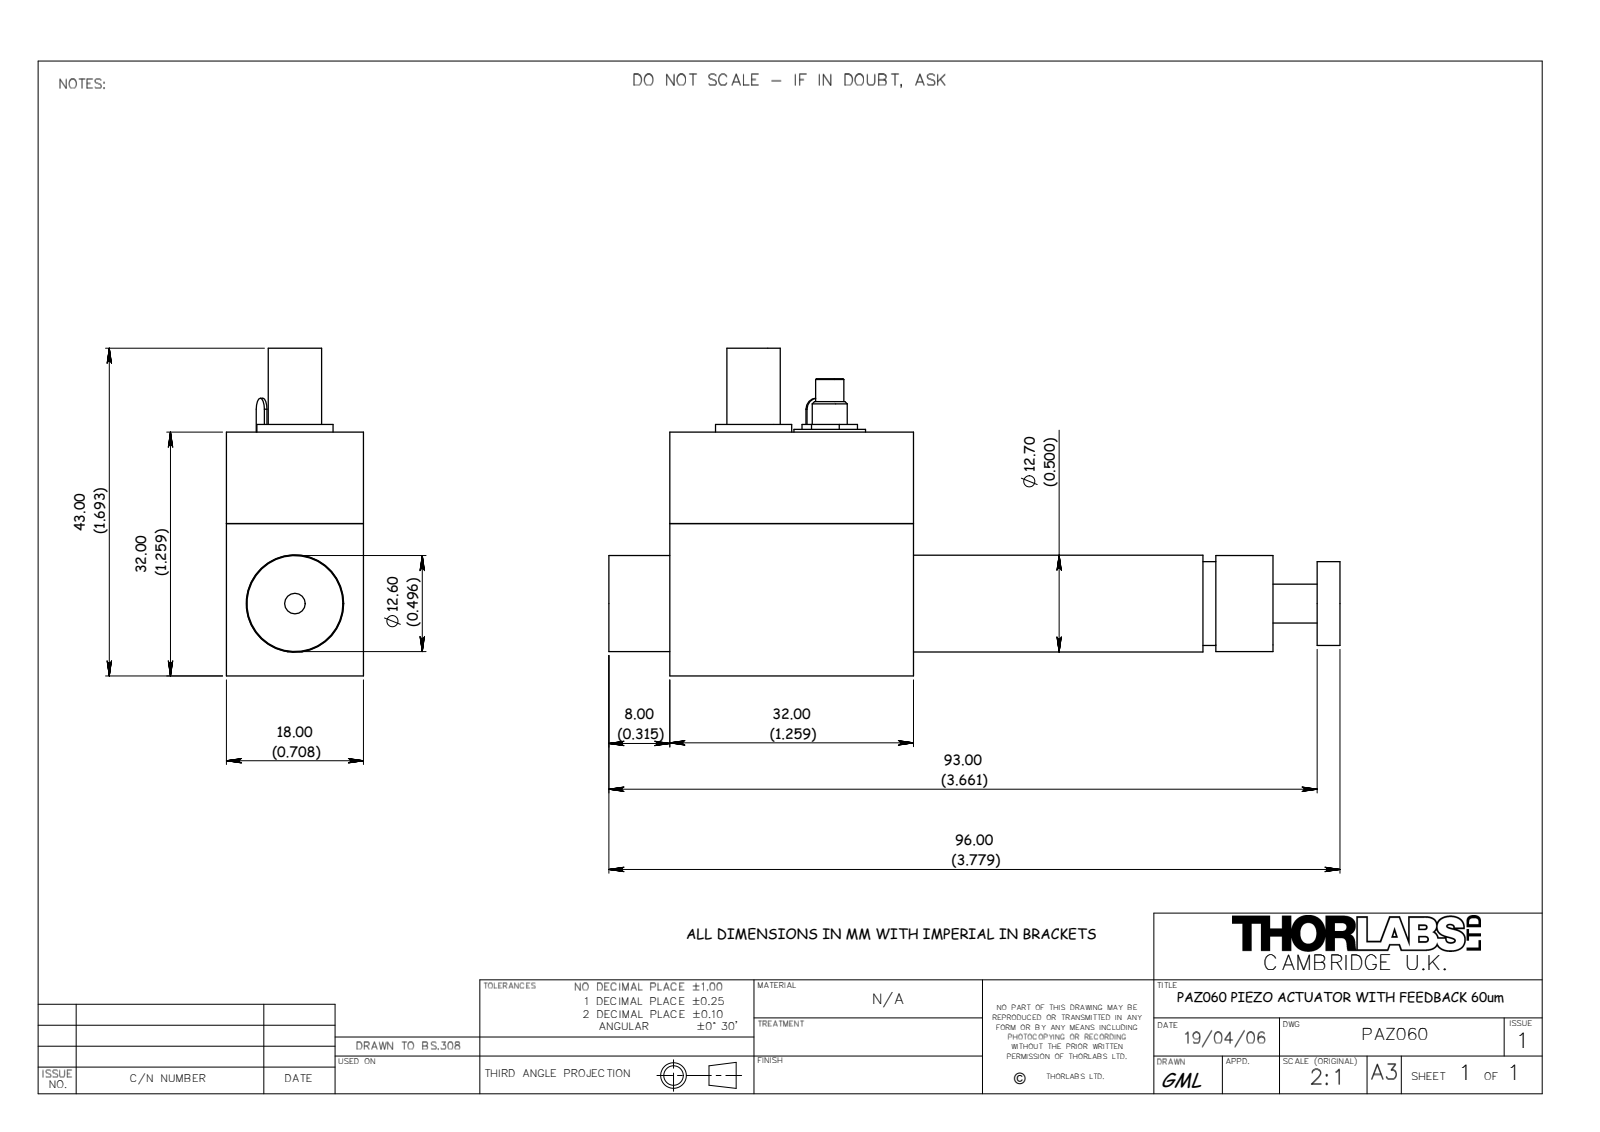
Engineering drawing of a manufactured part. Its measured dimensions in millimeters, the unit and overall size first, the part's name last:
Units: millimetres
Overall size (bounding box): 96 × 42.85 × 18
Round holes (diameter × count): ⌀5 ×2, ⌀2.71 ×1, ⌀3 ×1, ⌀5.3 ×1, ⌀11.4 ×1
Round bosses / shafts (diameter × count): ⌀12.7 ×1, ⌀12.6 ×1, ⌀11 ×1, ⌀10 ×1, ⌀9.4 ×1, ⌀9 ×1, ⌀7 ×1, ⌀5.1 ×1
Partial cylindrical surfaces — rounded edges, fillets, slot ends (radius × count): R1.44 ×1
Main face-to-face distances: 18, 32, 40, 8, 47.2, 79.2, 87.2, 8.8, 56, 88
Hole centre spacings: 8, 18, 26
Bodies: 0 solids, 115 faces (64 planar, 39 cylindrical, 12 other)
Part name (STEP PRODUCT): 15668-E0W
STEP written by: SolidWorks 2007 (AUTOMOTIVE_DESIGN)
